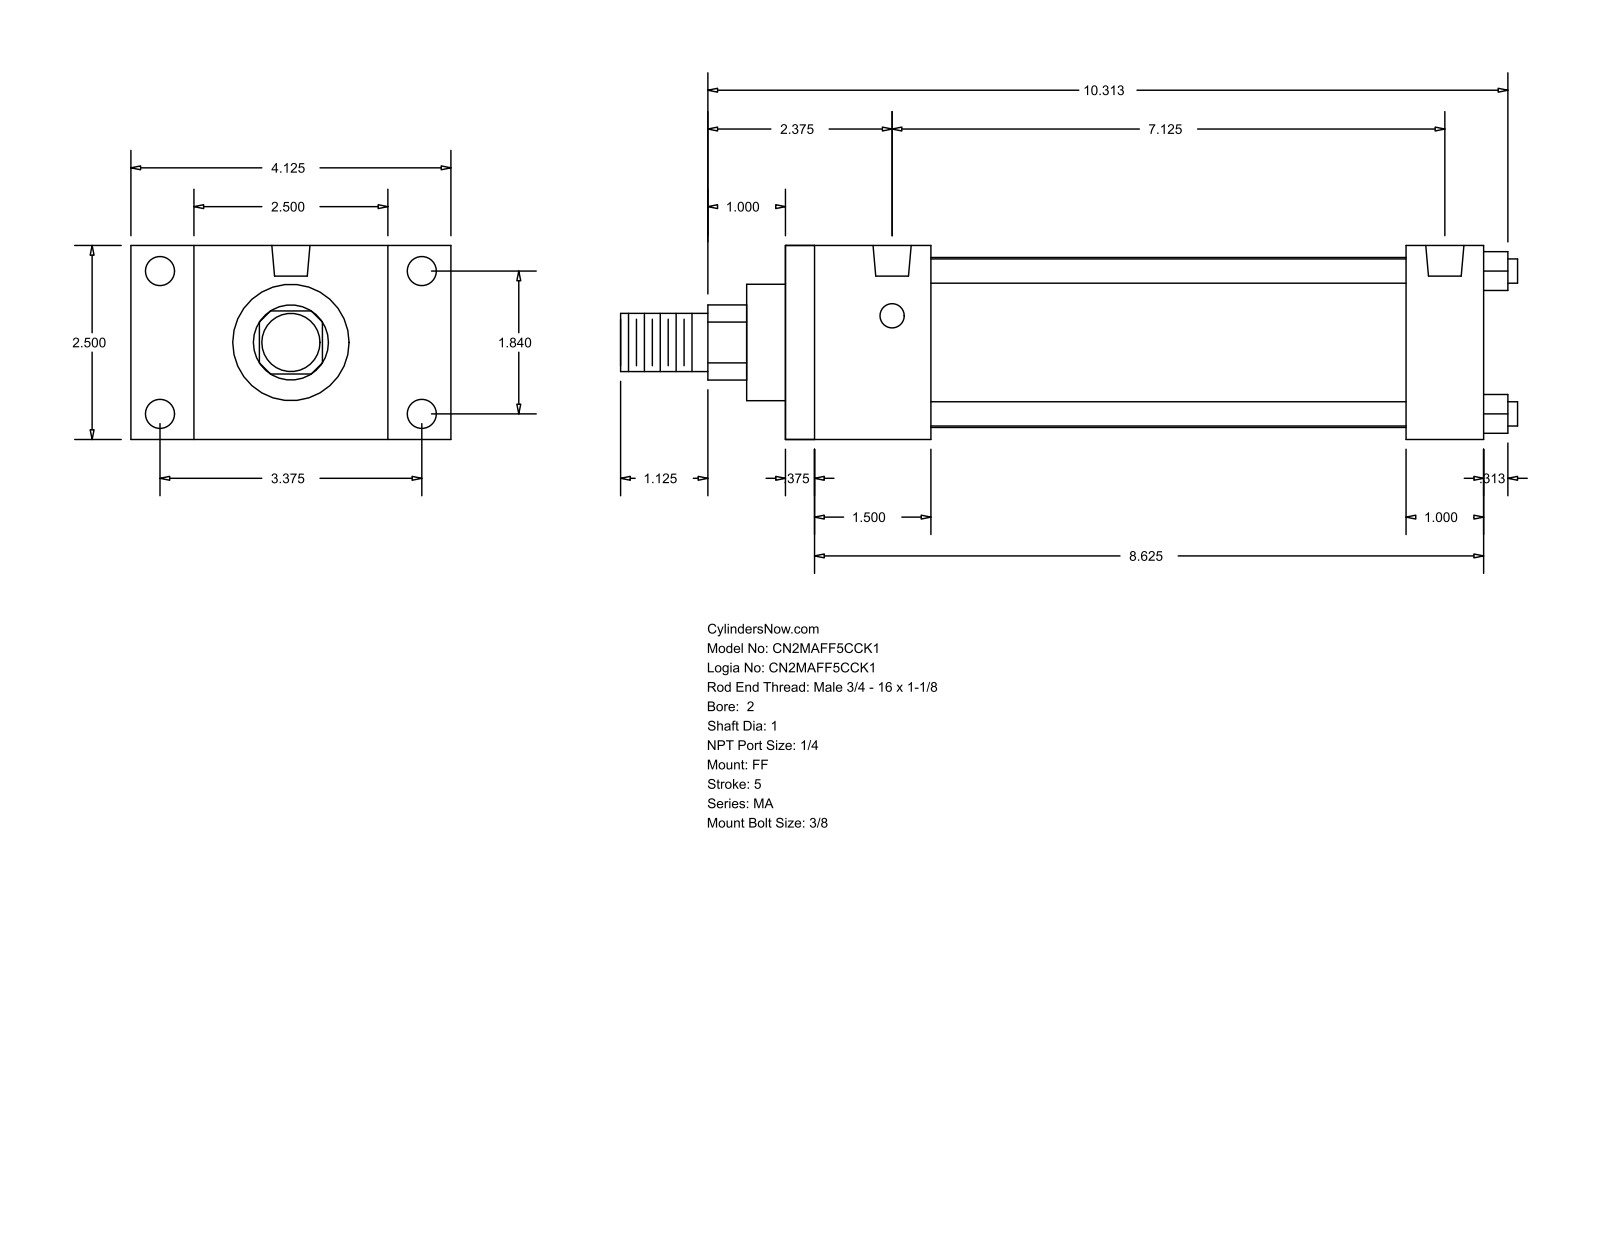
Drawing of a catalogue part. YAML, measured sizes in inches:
part_name: "MA_FF__0200_1"
step_written_by: "GSSL Pune (CONFIG_CONTROL_DESIGN)"
units: inches
bodies: {solids: 0, faces: 92, planar: 64, cylindrical: 28, other: 0}
overall_size: [11.563, 4.125, 2.5]
round_holes:
  - {diameter: 0.313, count: 4}
  - {diameter: 0.375, count: 4}
  - {diameter: 0.492, count: 2}
round_bosses_or_shafts:
  - {diameter: 0.313, count: 4}
  - {diameter: 2.19, count: 1}
  - {diameter: 1.5, count: 1}
  - {diameter: 1, count: 1}
  - {diameter: 0.75, count: 1}
partial_cylinders:
  - {radius: 0.484, count: 1}
face_to_face_distances: [2.5, 9, 0.375, 8.625, 1, 0.813, 0.5, 1.875, 8, 1.5]
hole_center_spacings: [1.84, 3.375, 3.844, 7.125]
